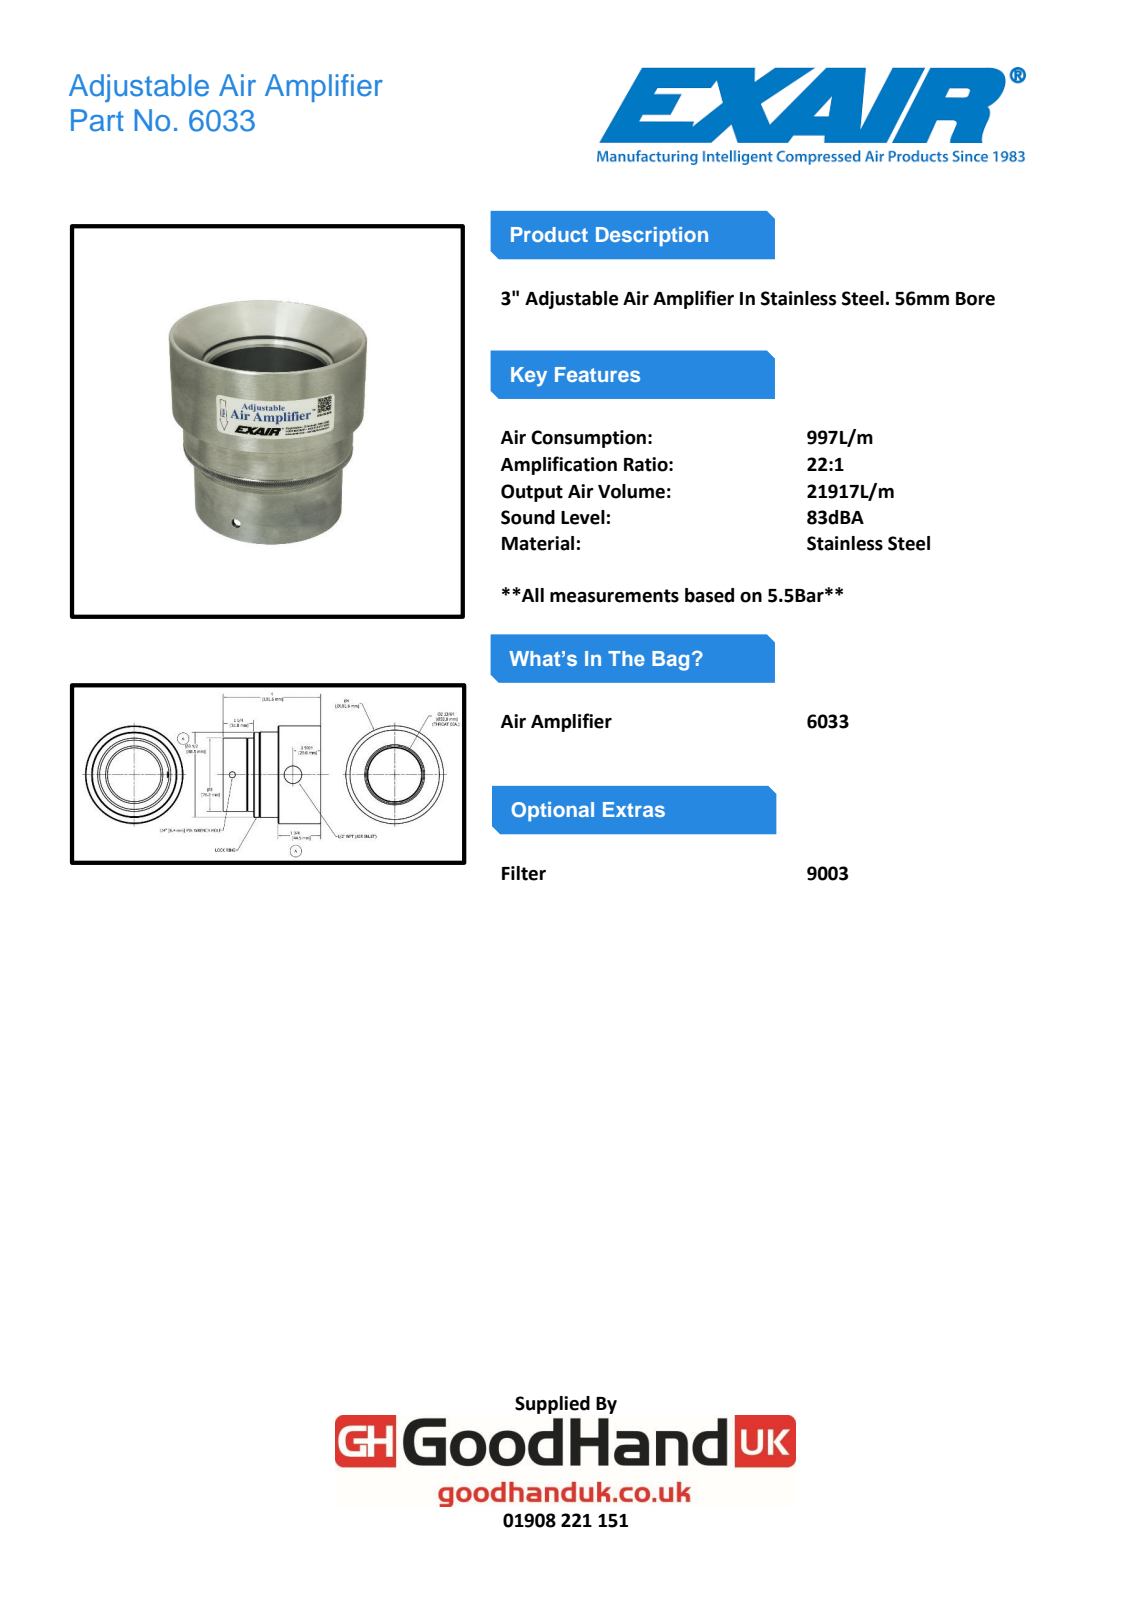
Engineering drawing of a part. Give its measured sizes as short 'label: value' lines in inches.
written by: Autodesk Inventor 2010 (AUTOMOTIVE_DESIGN)
unit: in
bodies: 3 solids, 27 faces (6 planar, 9 cylindrical, 12 other)
size: 4.081 × 4 × 4
volume: 23.81 in³; area: 136 in²
holes: 1× ⌀0.25, 1× ⌀0.719, 1× ⌀2.46
bosses: 1× ⌀4, 1× ⌀3.5, 1× ⌀3.484, 1× ⌀3
face distances: 0.75, 1.875, 1.125, 0.25, 1, 2.125, 1.25, 1.5, 2.25, 3.375
hole spacings: 2.485
